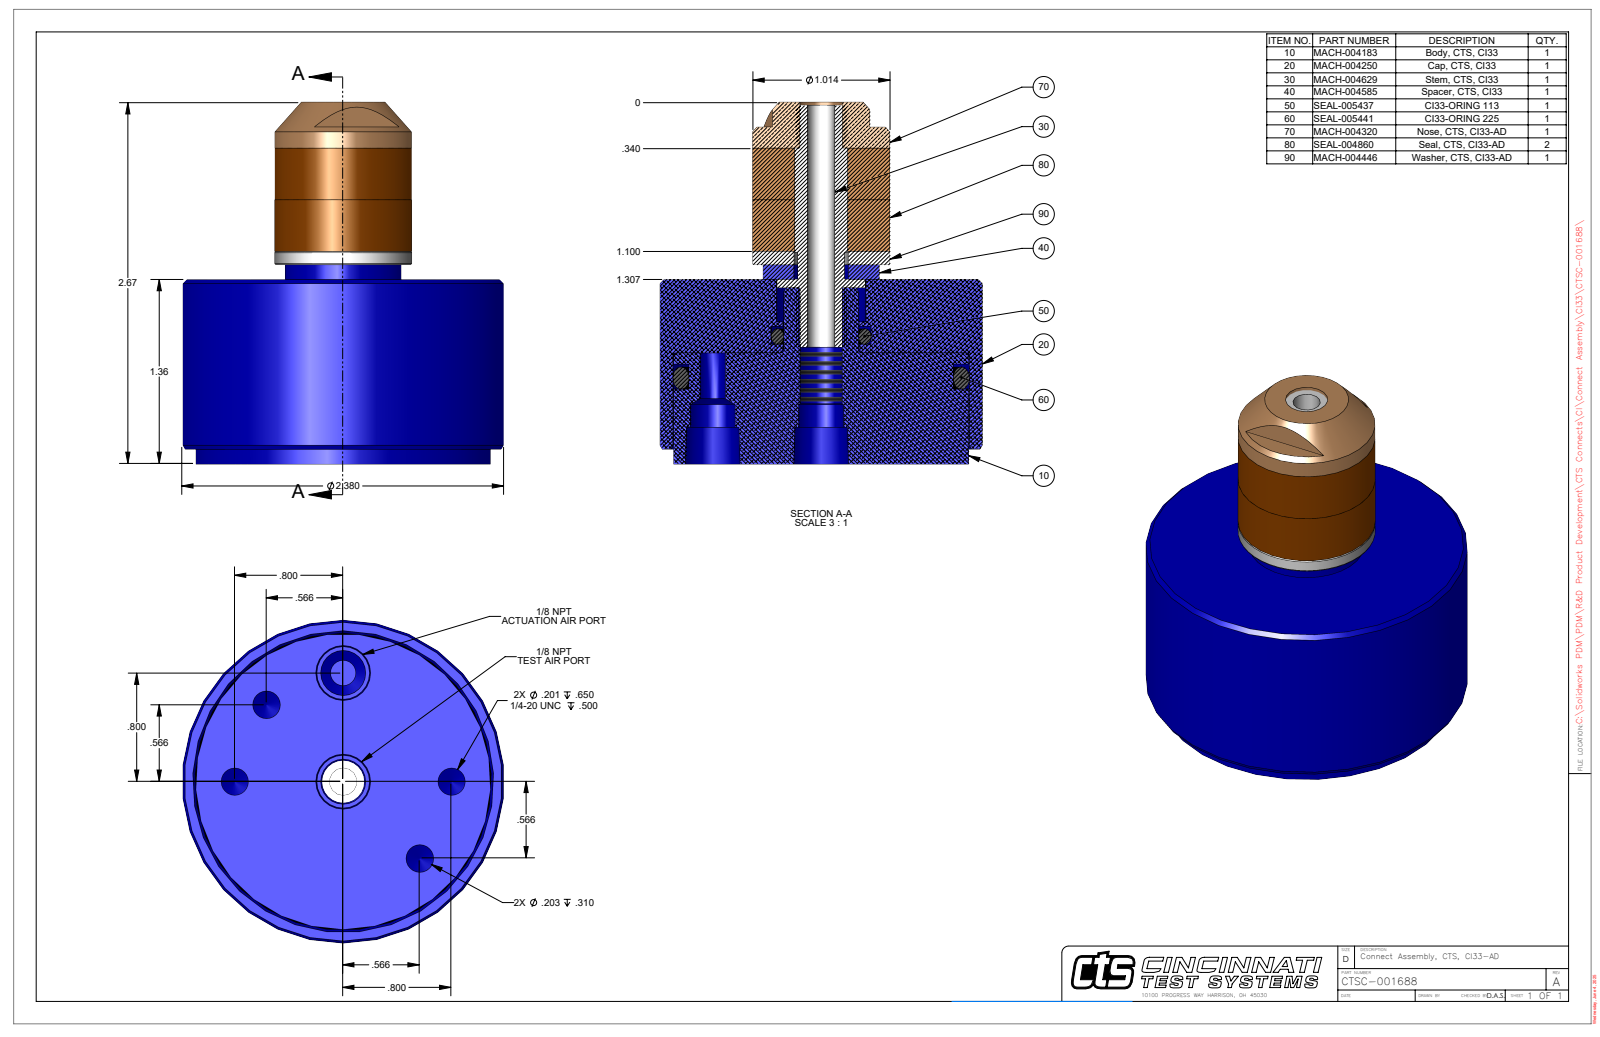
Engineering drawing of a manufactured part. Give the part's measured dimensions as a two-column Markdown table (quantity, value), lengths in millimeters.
| quantity | value |
| --- | --- |
| part name | CTSC-001688 |
| STEP written by | SolidWorks 2023 (AUTOMOTIVE_DESIGN) |
| units | millimeters |
| bodies | 1 solid, 76 faces (20 planar, 32 cylindrical, 24 other) |
| overall size | 67.7 × 60.5 × 60.5 |
| volume | 109 700 mm³ |
| surface area | 19 960 mm² |
| round holes (diameter × count) | 5.1 × 2, 5.2 × 2, 8.4 × 2, 5.2 × 1, 8 × 1, 16.7 × 1, 55.6 × 1 |
| round bosses / shafts (diameter × count) | 60.5 × 1, 55.3 × 1, 25.8 × 1, 21.8 × 1, 16.5 × 1 |
| main face-to-face distances | 34.5, 2.8, 31.8, 67.7, 64.9, 33.2, 11.3, 8.5, 23.2, 56.4 |
| hole center spacings | 20.3, 15.5, 37.5, 28.7, 40.6 |
